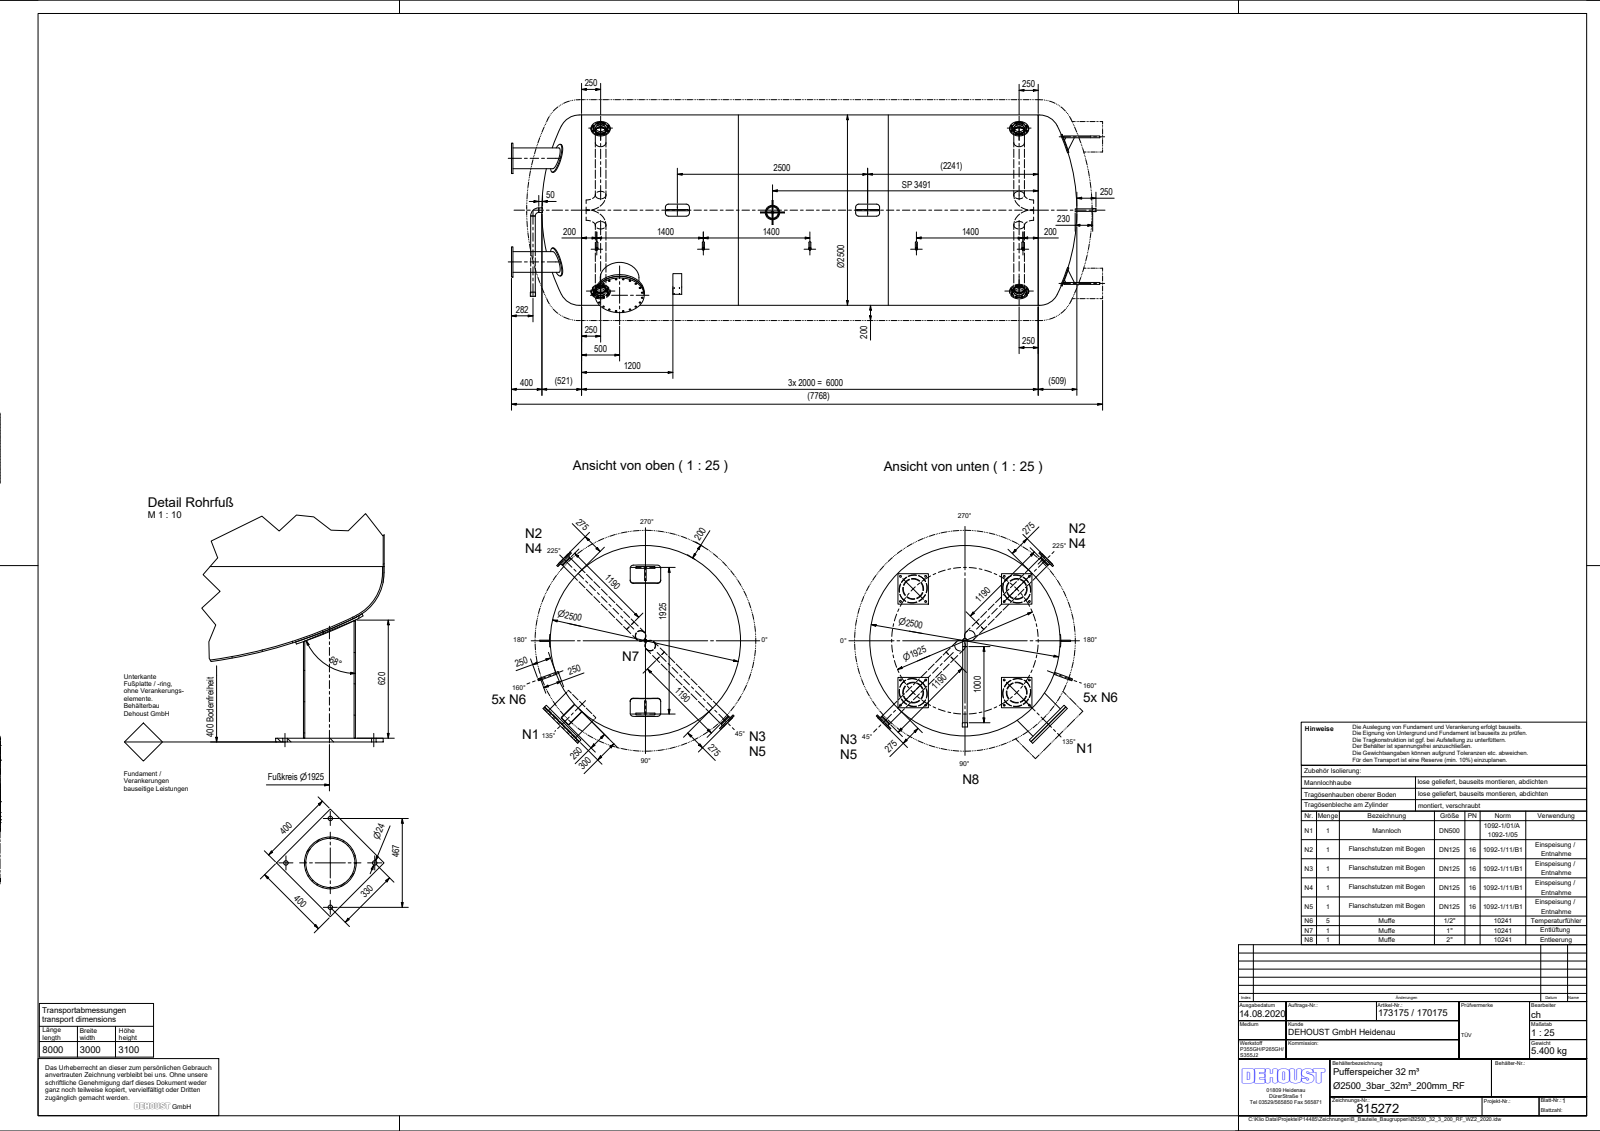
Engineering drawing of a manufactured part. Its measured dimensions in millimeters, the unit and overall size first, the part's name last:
Units: millimetres
Overall size (bounding box): 7732.1 × 2664.05 × 2595.98
Round holes (diameter × count): ⌀22 ×40, ⌀18 ×32, ⌀24 ×16, ⌀131.7 ×8, ⌀18.63 ×5, ⌀21.7 ×5, ⌀26.9 ×5, ⌀5.8 ×4, ⌀139.7 ×4, ⌀258.8 ×4, ⌀5 ×2, ⌀52.3 ×2
Round bosses / shafts (diameter × count): ⌀139.7 ×8, ⌀26.9 ×5, ⌀26.4 ×5, ⌀380 ×4, ⌀273 ×4, ⌀250 ×4, ⌀188 ×4, ⌀645 ×2
Partial cylindrical surfaces — rounded edges, fillets, slot ends (radius × count): R42 ×16, R6 ×8, R5 ×2, R10 ×2, R36 ×2, R72 ×2, R125 ×1, R1259 ×1
Main face-to-face distances: 20, 600, 3778.97, 4153.97, 3758.97, 4133.97, 375, 27.99, 25, 650
Hole centre spacings: 105, 300, 93.86, 185.41, 1400, 352.67, 5500, 485.41
Volume: 529 400 000 mm³ · Surface area: 137 100 000 mm²
Bodies: 58 solids, 449 faces (178 planar, 225 cylindrical, 46 other)
Part name (STEP PRODUCT): Ø2500_32_3_200_RF_WZ2_2020; Klöpper_Gew_Ø2500_5,5; Klöpper_Gew_Ø2500_8,3; Zyl_Ø2500_5x6000_2020 (+8 more)
STEP written by: Autodesk Inventor 2019 (AUTOMOTIVE_DESIGN)
